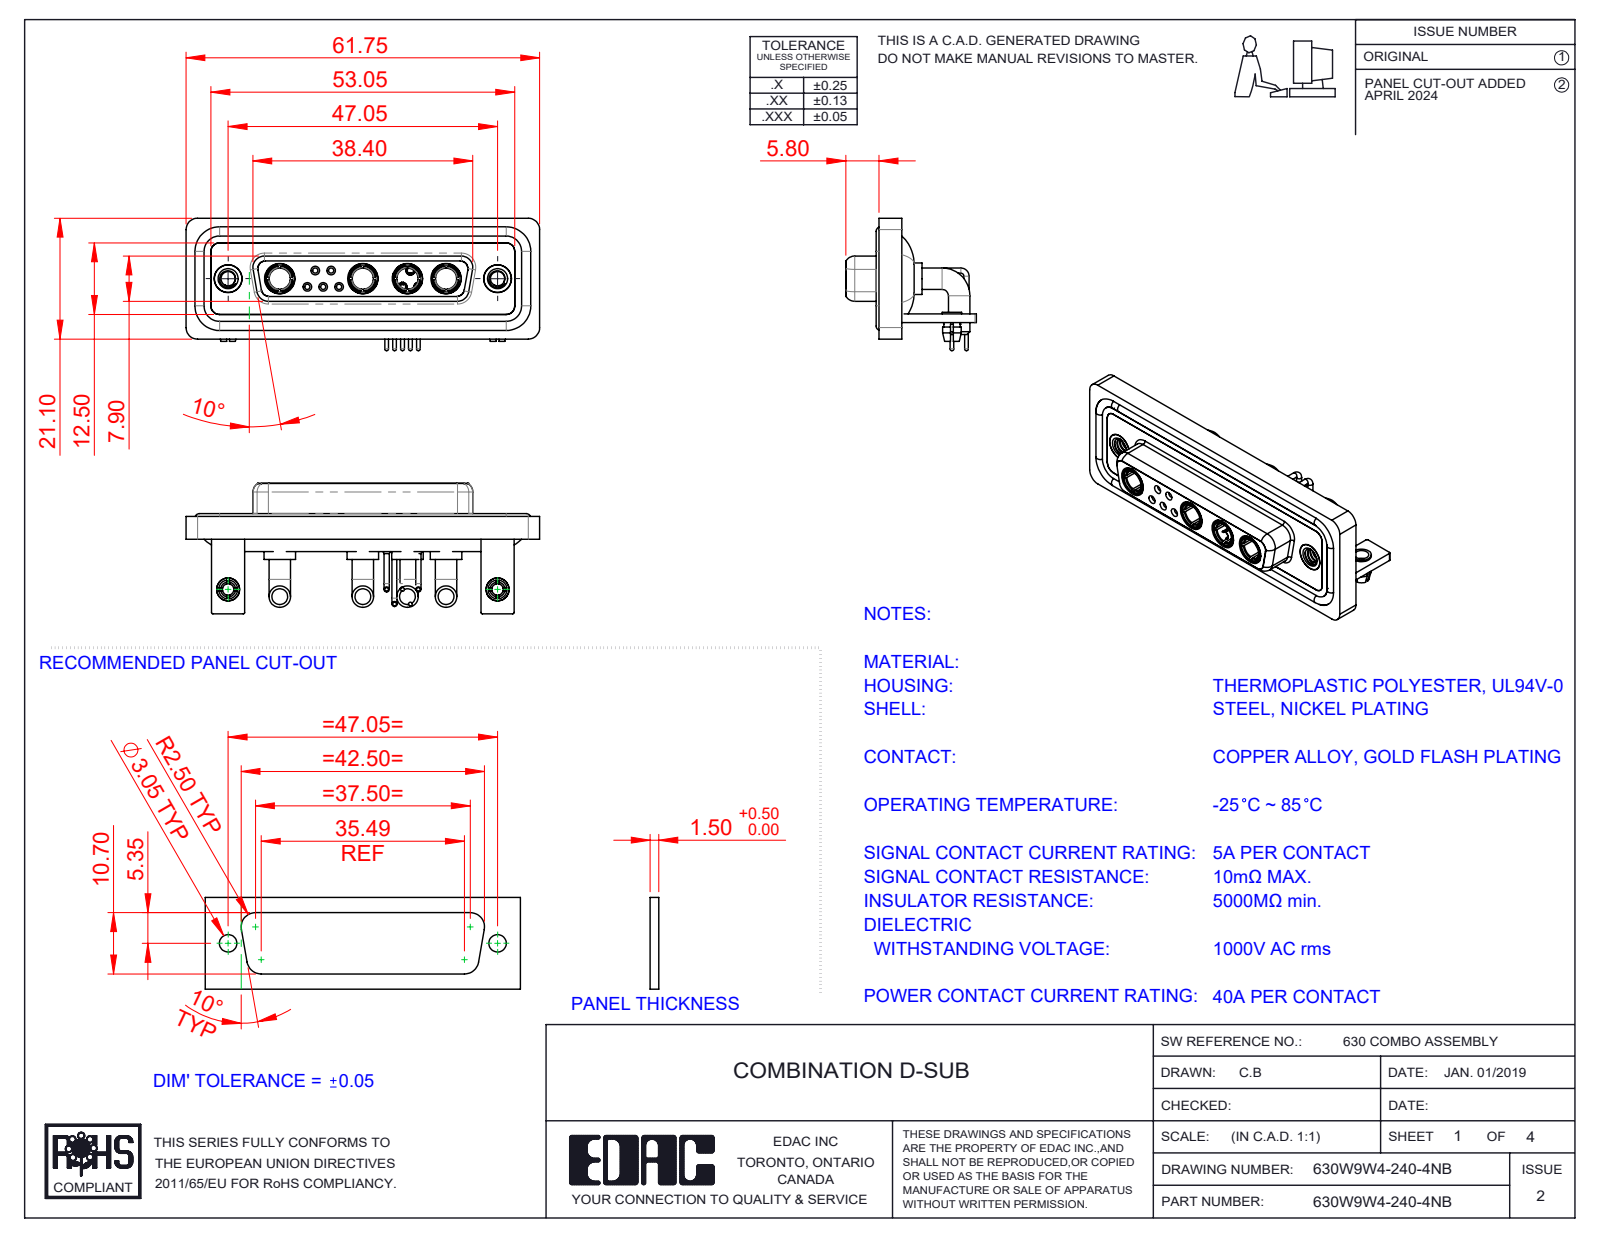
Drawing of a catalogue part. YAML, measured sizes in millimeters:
part_name: "630Combo Contact Row 1_50 Contacts; Power Socket_40A RA; 630Combo Contact Row 2_50 Contacts; 630Combo Stabilizer Bracket_50 Contacts (+7 more)"
step_written_by: "SolidWorks 2023 (CONFIG_CONTROL_DESIGN)"
units: millimeters
bodies: {solids: 24, faces: 1097, planar: 364, cylindrical: 457, other: 276}
overall_size: [61.75, 23.12, 22.8]
volume: 9138
surface_area: 15171
round_holes:
  - {diameter: 2, count: 7}
  - {diameter: 4.85, count: 6}
  - {diameter: 0.9, count: 5}
  - {diameter: 1.1, count: 5}
  - {diameter: 1.5, count: 5}
  - {diameter: 2.5, count: 4}
  - {diameter: 3.7, count: 4}
  - {diameter: 5.3, count: 4}
  - {diameter: 1.6, count: 3}
  - {diameter: 1.7, count: 2}
  - {diameter: 3.2, count: 2}
  - {diameter: 4, count: 2}
round_bosses_or_shafts:
  - {diameter: 0.9, count: 10}
  - {diameter: 1.6, count: 9}
  - {diameter: 3.75, count: 8}
  - {diameter: 2, count: 5}
  - {diameter: 1.5, count: 5}
  - {diameter: 0.65, count: 5}
  - {diameter: 5.5, count: 4}
  - {diameter: 5.2, count: 4}
partial_cylinders:
  - {radius: 2, count: 19}
  - {radius: 1.5, count: 18}
  - {radius: 0.25, count: 16}
  - {radius: 1.35, count: 8}
  - {radius: 1.6, count: 8}
  - {radius: 0.5, count: 5}
  - {radius: 0.6, count: 4}
  - {radius: 0.65, count: 4}
face_to_face_distances: [0.4, 1.8, 2.9, 3.7, 1.5, 4.1, 1.1, 1.4, 1.6, 2.5]
hole_center_spacings: [3.16, 2.77, 5.04, 13.85, 11.08, 12.79, 15.5, 5.54]
